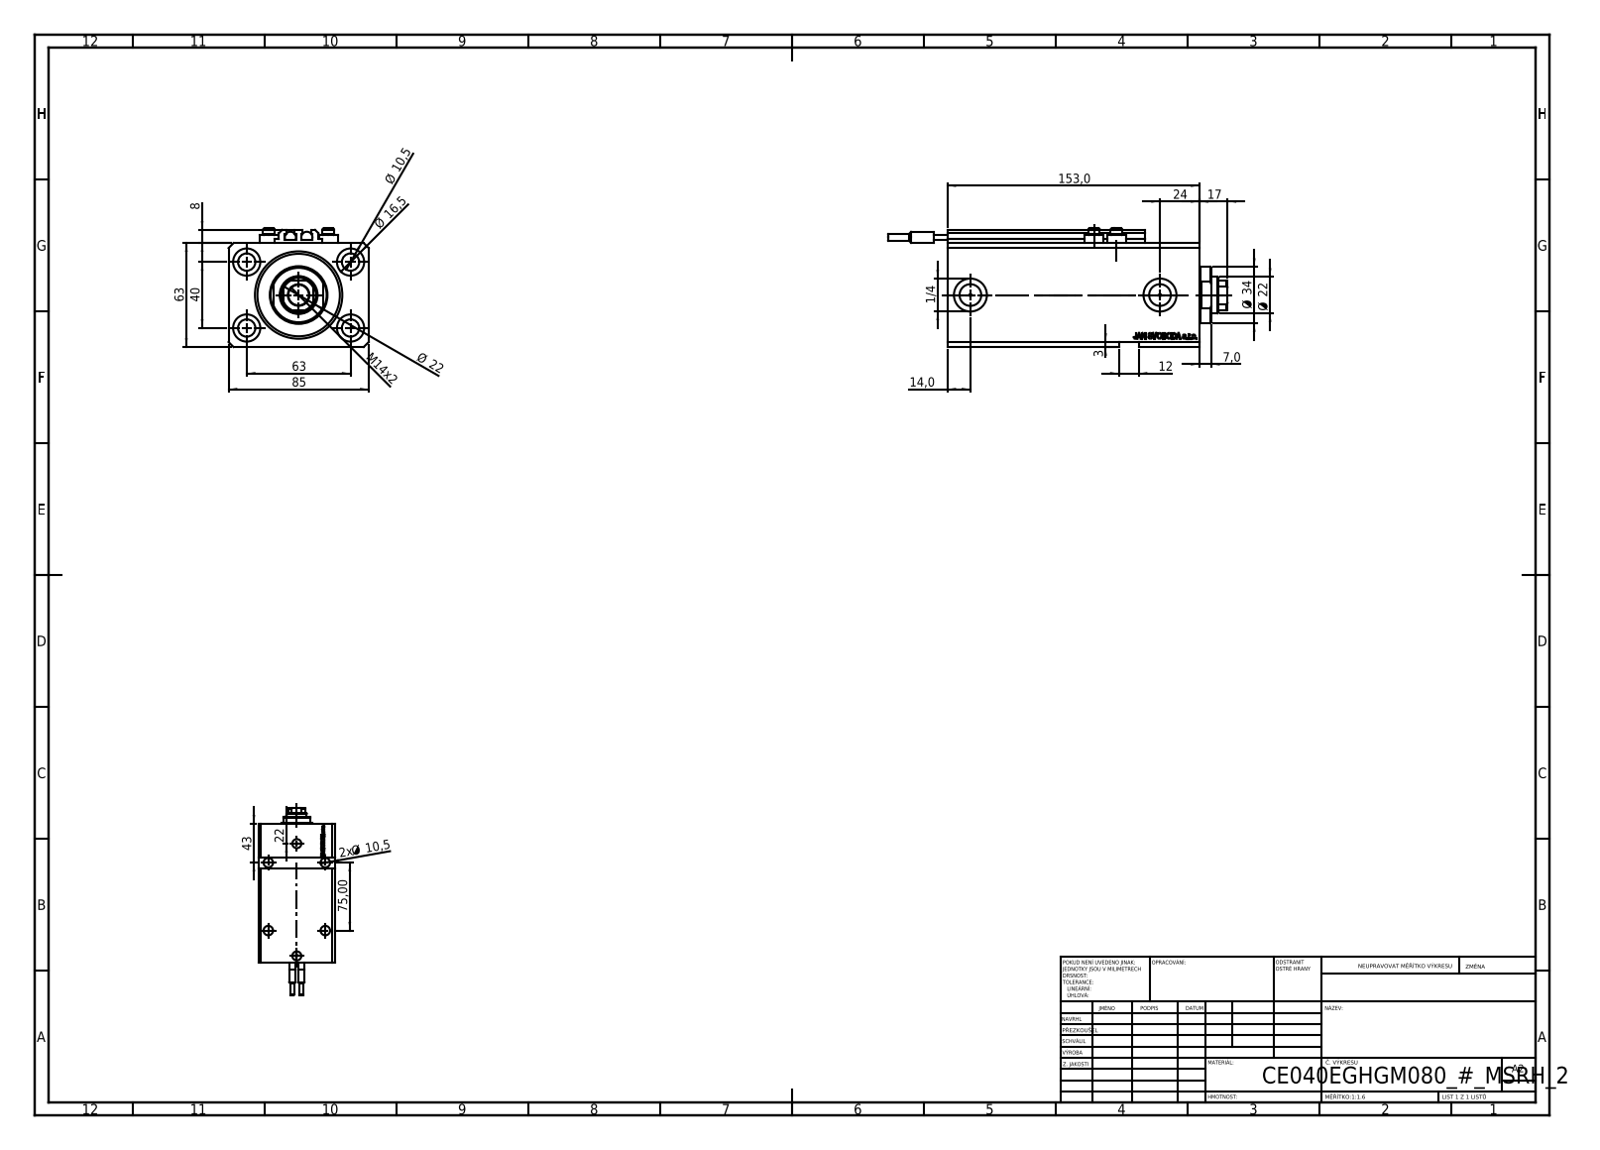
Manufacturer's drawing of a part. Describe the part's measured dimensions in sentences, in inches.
The part is named "V250CE_VC_E; V250CE_C_VCP; ALLEN BOLT V250CE; V250CE_E_Body (+1 more)". Its 3-D file was written by "SolidWorks 2019 (CONFIG_CONTROL_DESIGN)". It is 10 solids with 1159 faces: 567 planar, 158 cylindrical and 434 other. Overall it measures 8.11 by 3.346 by 2.835 inches. Its volume is 41.95 cubic inches and its surface area 222.5 square inches. Round holes: 8 of diameter 0.413, 4 of diameter 0.049, 4 of diameter 0.157, 4 of diameter 0.65, 2 of diameter 0.394, 2 of diameter 0.518, 2 of diameter 0.787, 1 of diameter 0.492, 1 of diameter 0.866, 1 of diameter 1.575, 1 of diameter 2.087. Round bosses or shafts: 4 of diameter 0.457, 4 of diameter 0.276, 2 of diameter 0.268, 2 of diameter 0.256, 2 of diameter 0.157, 1 of diameter 1.339. Partial cylindrical surfaces (rounded edges, fillets, slot ends): 10 of radius 0.008, 1 of radius 0.413. The main face-to-face distances are 2.48, 3.346, 6.024, 0.669, 5.354, 0.118, 2.559, 0.449, 4.906, 5.575. The hole center spacings are 1.469, 2.48, 0.535, 0.606, 0.983, 1.324, 1.417, 1.491.
